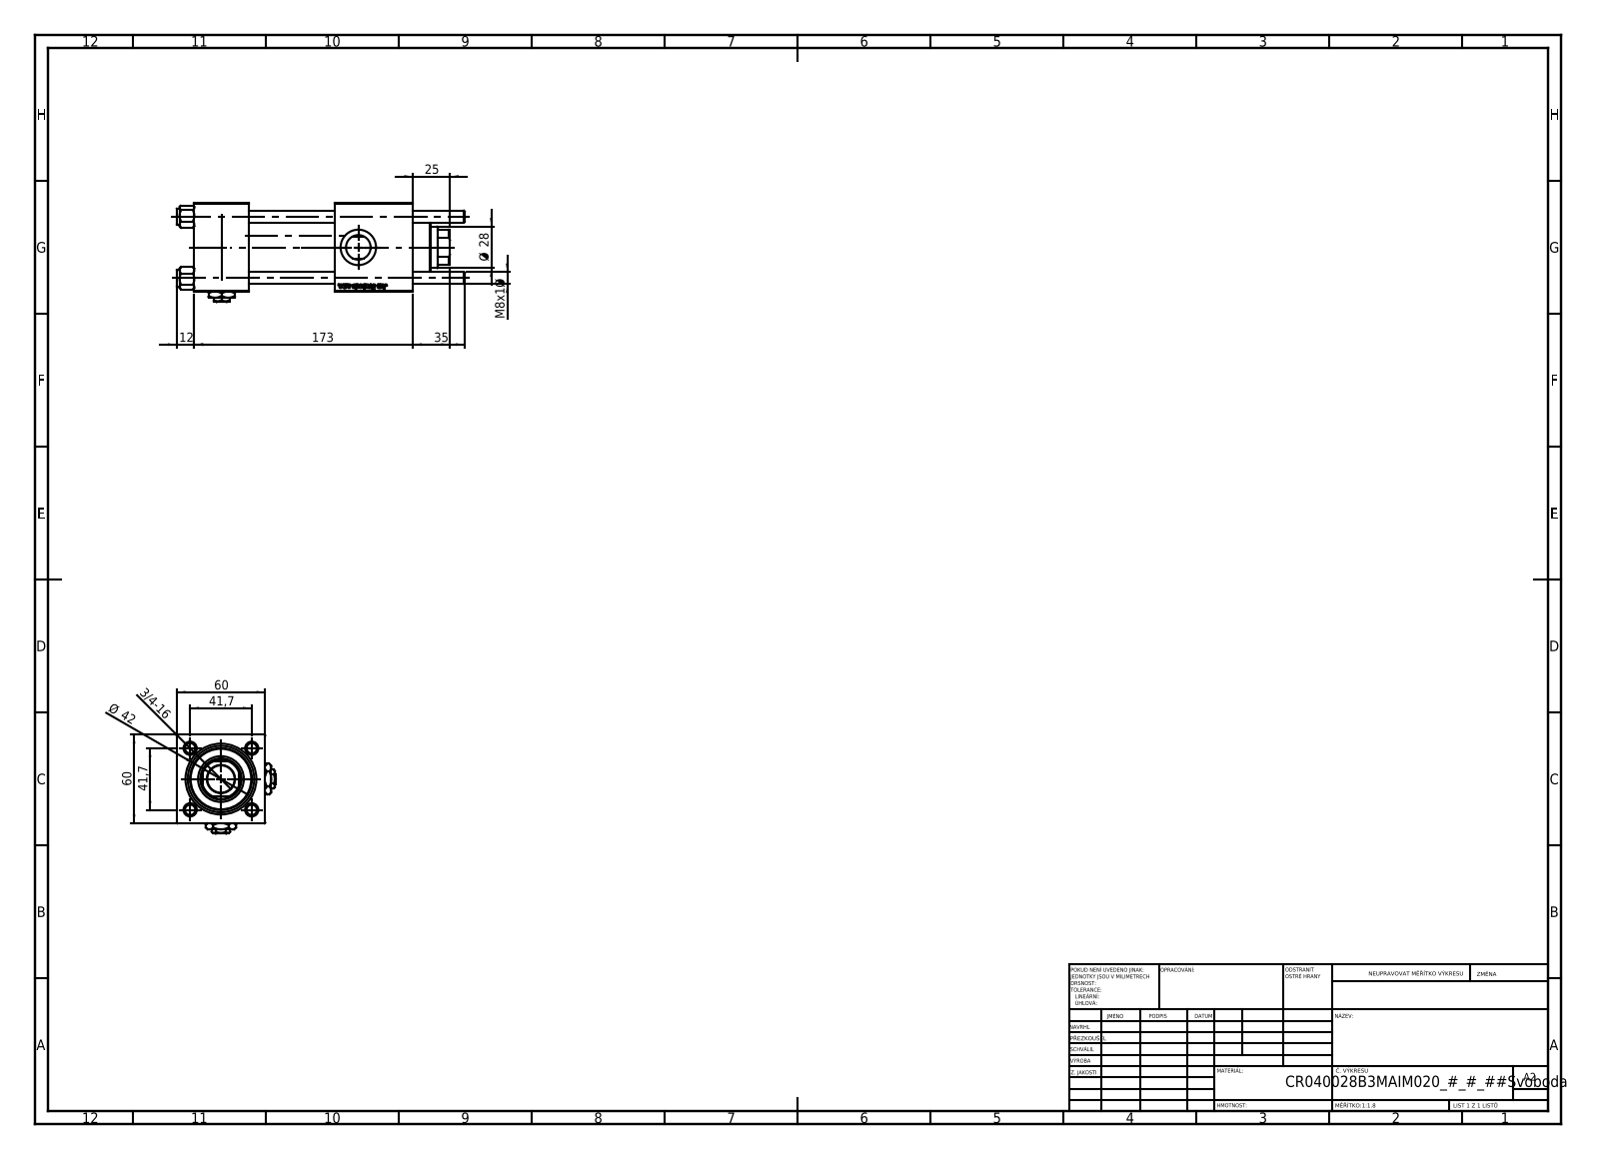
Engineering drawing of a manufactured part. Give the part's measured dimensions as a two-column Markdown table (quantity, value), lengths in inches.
| quantity | value |
| --- | --- |
| part name | Zatka_pro_OIL_PORT; NUT_M5_B; V215CR_B-1; V215CR_B_TYCINKA (+2 more) |
| STEP written by | SolidWorks 2019 (CONFIG_CONTROL_DESIGN) |
| units | inches |
| bodies | 13 solids, 1260 faces (480 planar, 90 cylindrical, 690 other) |
| overall size | 7.677 × 2.638 × 2.638 |
| volume | 26.34 in³ |
| surface area | 190.6 in² |
| round holes (diameter × count) | 0.315 × 4, 0.276 × 2, 0.656 × 2, 0.945 × 2, 0.63 × 1, 0.728 × 1, 1.102 × 1, 1.22 × 1, 1.575 × 1, 1.772 × 1 |
| round bosses / shafts (diameter × count) | 0.433 × 4, 1.811 × 1, 1.654 × 1 |
| partial cylindrical surfaces (radius × count) | 0.531 × 1 |
| main face-to-face distances | 2.362, 1.457, 2.283, 3.74, 2.087, 4.697, 3.24, 0.957, 5.827, 4.37 |
| hole center spacings | 1.161, 1.642, 2.322 |
